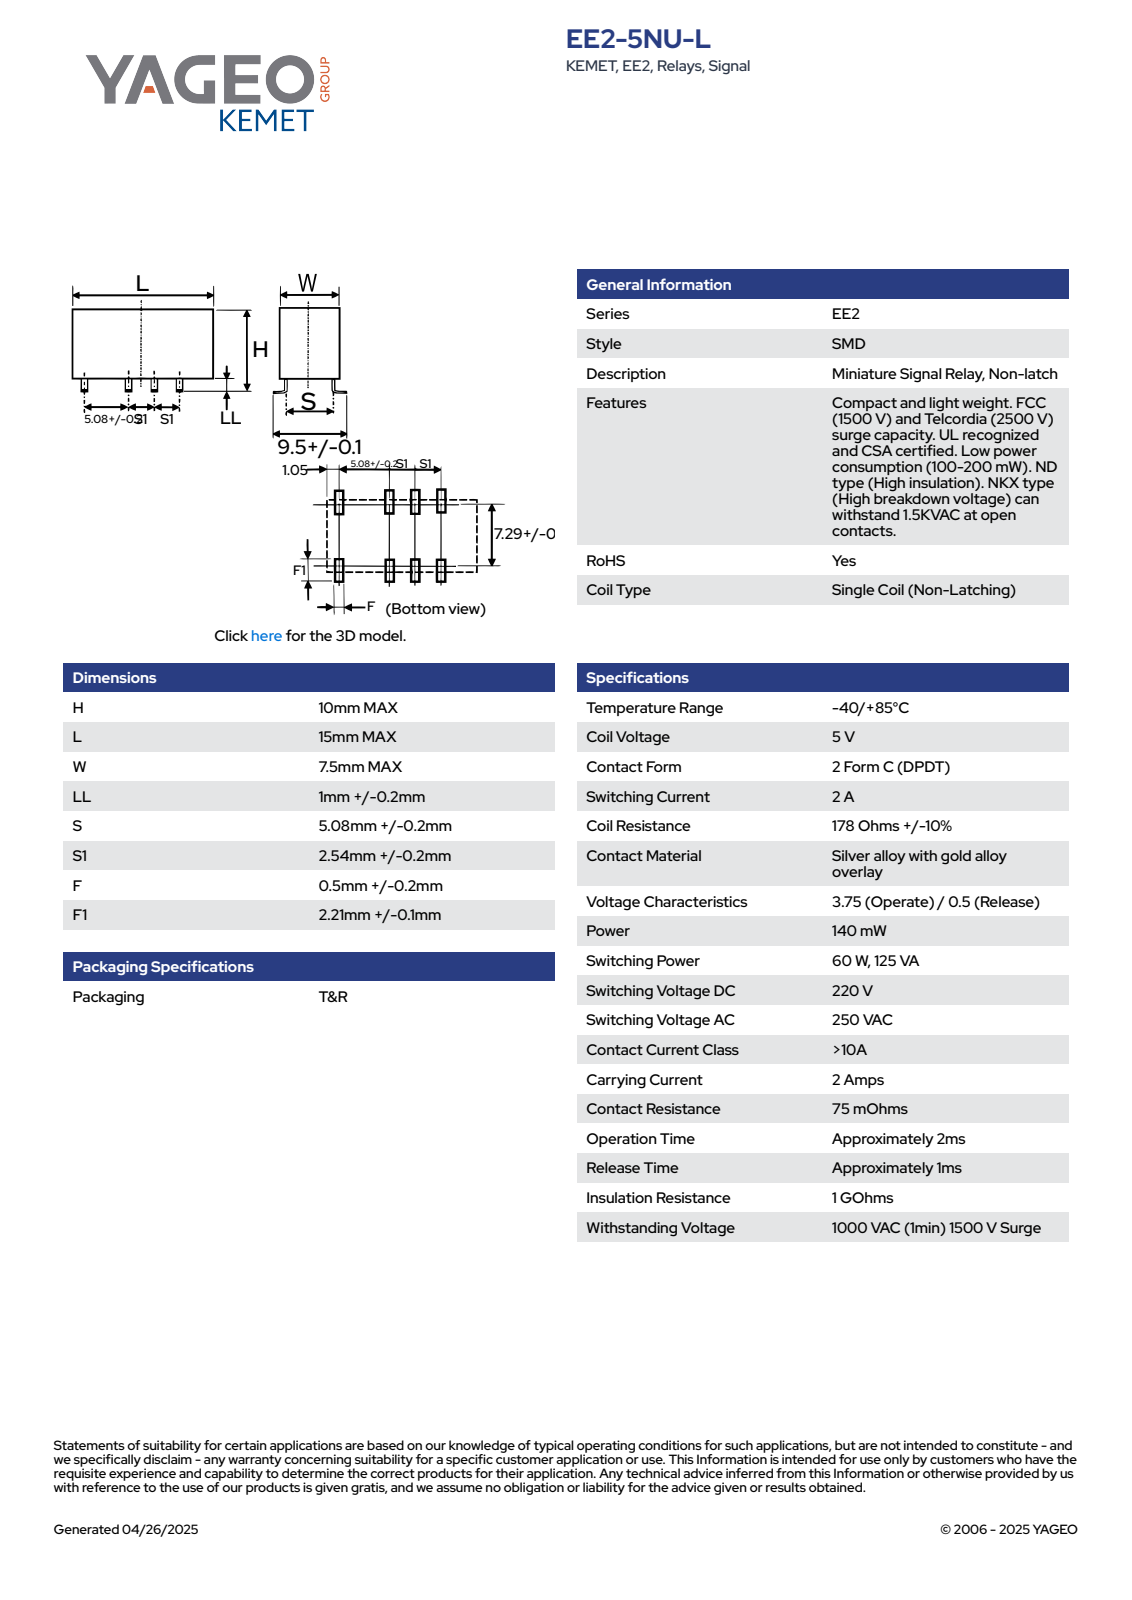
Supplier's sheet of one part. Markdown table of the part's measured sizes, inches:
| quantity | value |
| --- | --- |
| part name | IR_TEE2STD_L15W7.5H10LL1.2 |
| STEP written by | SolidWorks 2014 (AUTOMOTIVE_DESIGN) |
| units | inches |
| bodies | 1 solid, 116 faces (116 planar, 0 cylindrical, 0 other) |
| overall size | 0.591 × 0.394 × 0.374 |
| volume | 0.061 in³ |
| surface area | 1.04 in² |
| main face-to-face distances | 0.295, 0.346, 0.591, 0.047, 0.394, 0.037, 0.384, 0.028, 0.052, 0.243 |
